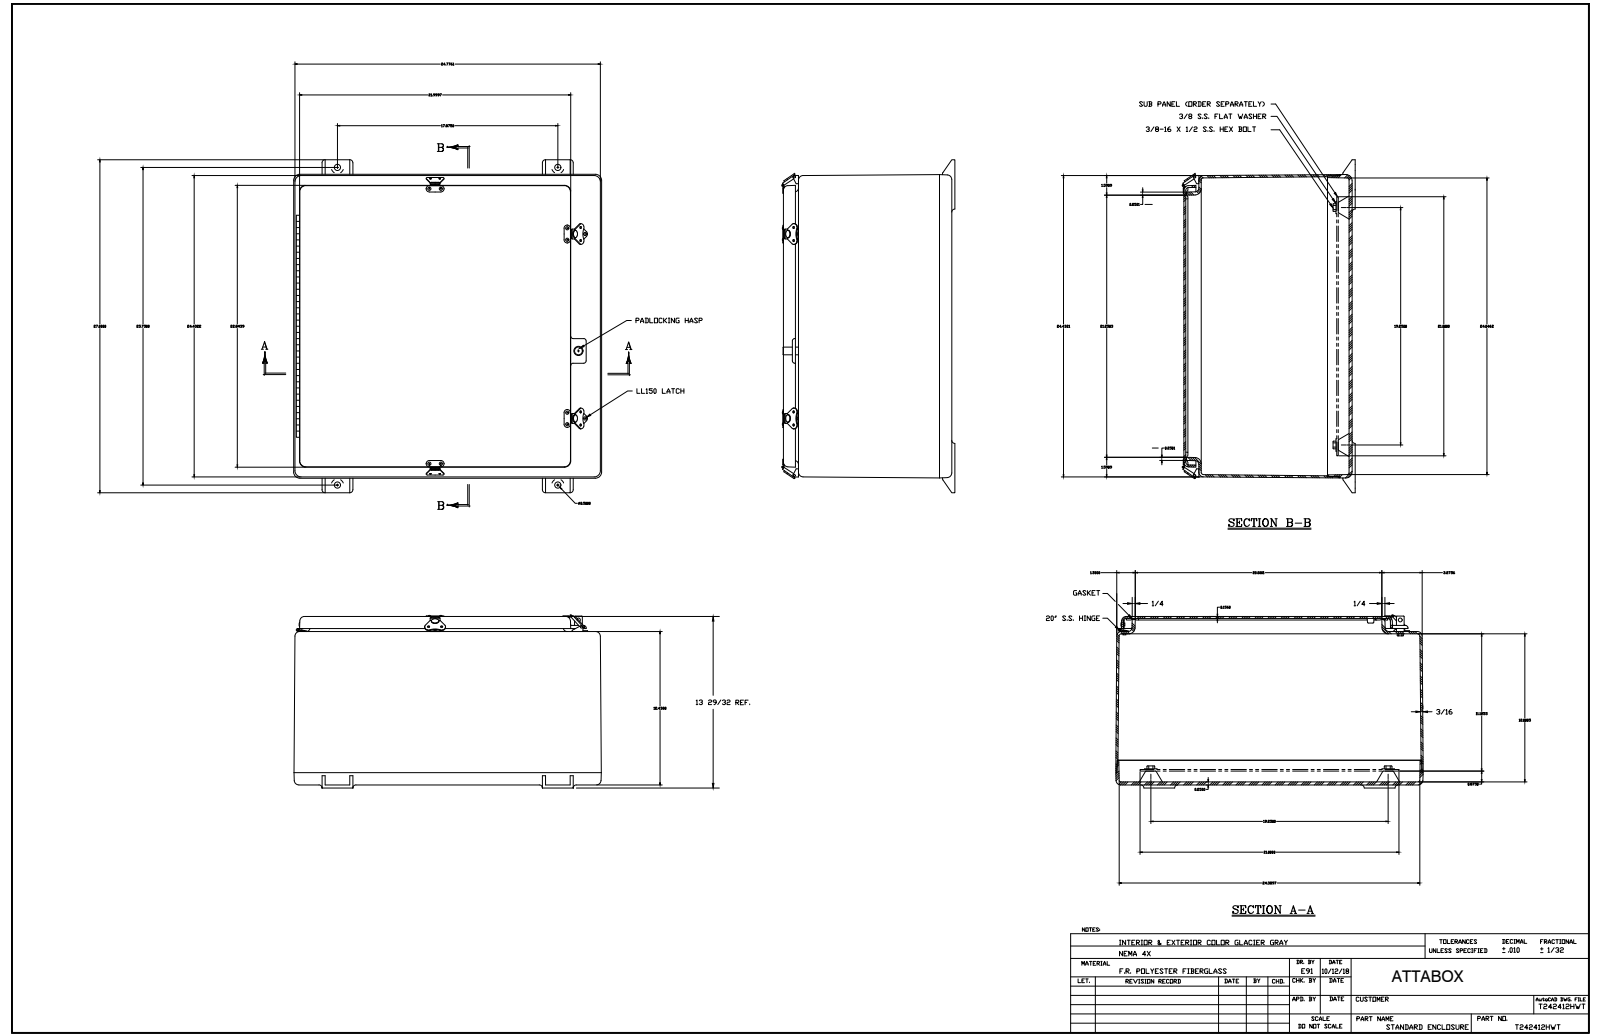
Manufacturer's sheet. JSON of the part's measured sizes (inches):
{"part_name": "T242412HWT", "step_written_by": "SolidWorks 2018 (AUTOMOTIVE_DESIGN)", "units": "inches", "bodies": {"solids": 56, "faces": 1475, "planar": 564, "cylindrical": 590, "other": 321}, "overall_size": [27, 24.981, 14.241], "volume_in3": 546, "surface_area_in2": 5797, "round_holes": [[0.13, 32], [0.063, 16], [0.138, 8], [0.187, 8], [0.065, 6], [0.281, 4], [0.563, 4], [0.156, 3], [0.065, 2], [0.135, 2], [0.145, 2], [0.51, 2]], "round_bosses_or_shafts": [[0.14, 16], [0.297, 8], [0.5, 4], [0.2, 3], [0.135, 2], [0.281, 1], [0.25, 1], [0.201, 1]], "partial_cylinders_radius": [[0.01, 101], [0.25, 20], [0.375, 20], [0.187, 18], [0.03, 16], [0.312, 16], [0.5, 12], [0.188, 11]], "face_to_face_distances": [0.25, 0.187, 0.156, 0.188, 13.406, 13.656, 13.5, 13.25, 12.437, 12.25], "hole_center_spacings": [5.25, 11.75, 6.5, 17, 0.937, 1, 1.512, 3.322]}
